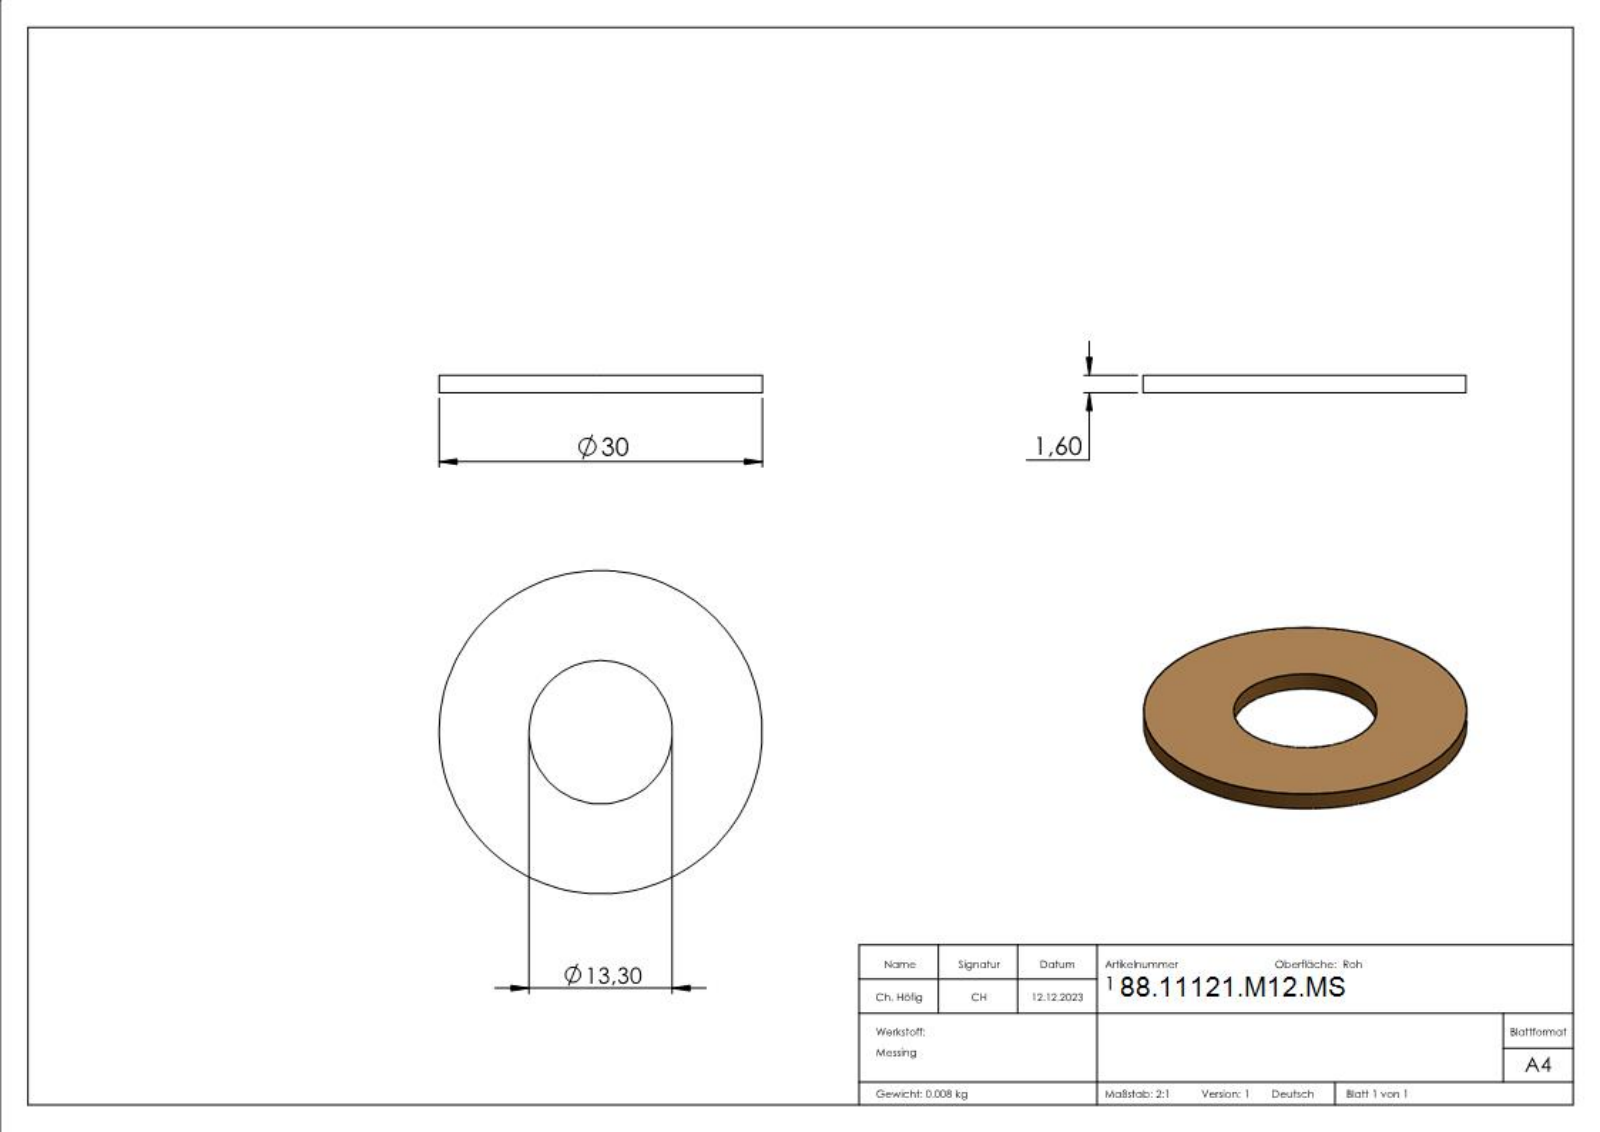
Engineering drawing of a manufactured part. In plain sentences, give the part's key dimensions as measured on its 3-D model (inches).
The part is named "121-M12-MS". Its 3-D file was written by "SolidWorks 2018 (CONFIG_CONTROL_DESIGN)". It is 1 solid with 263 faces: 166 planar, 2 cylindrical and 95 other. Overall it measures 1.181 by 1.181 by 0.063 inches. Its volume is 0.055 cubic inches and its surface area 2.111 square inches. Round holes: 1 of diameter 0.524. Round bosses or shafts: 1 of diameter 1.181. The main face-to-face distances are 0.063, 0.059, 0.091, 0.013, 0.087, 0.013, 0.077, 0.064, 0.101, 0.764.
